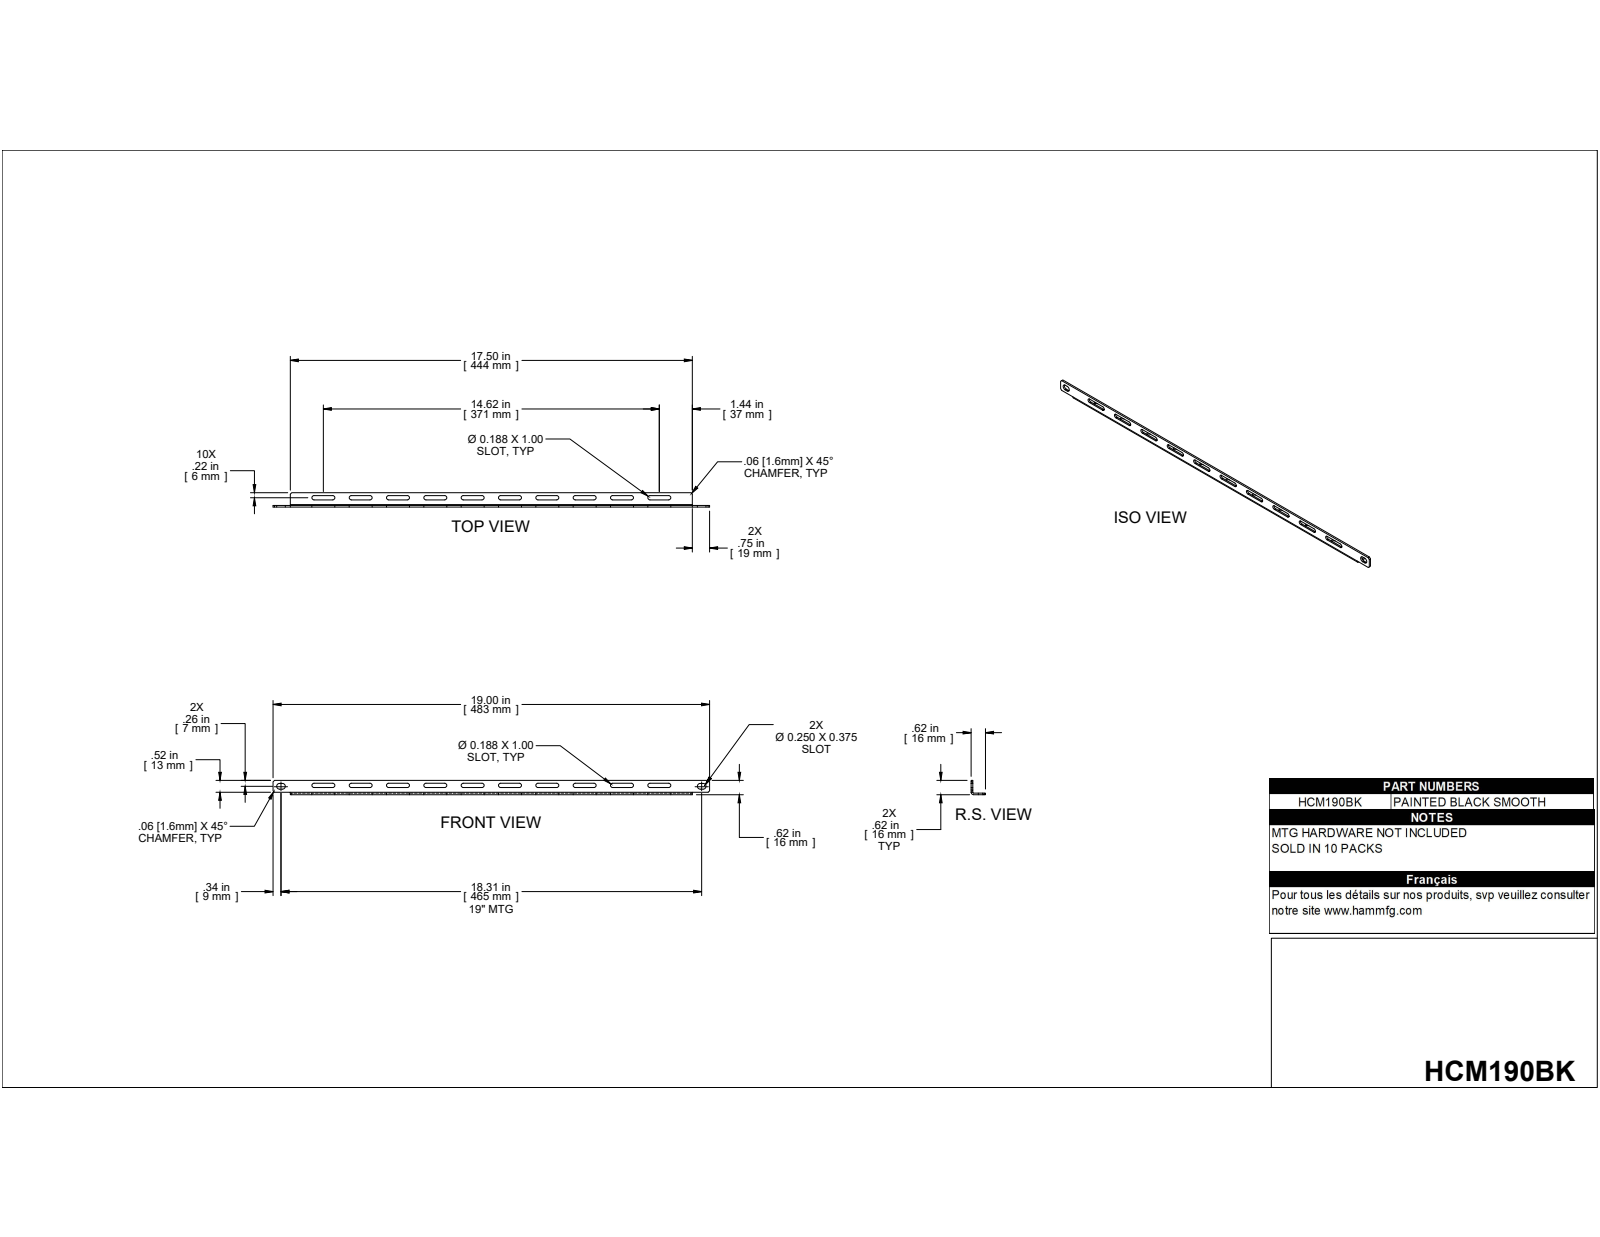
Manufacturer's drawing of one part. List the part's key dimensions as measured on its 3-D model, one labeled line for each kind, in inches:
Part name (STEP PRODUCT): COM57141-1
STEP written by: ST-DEVELOPER v16.7 (AUTOMOTIVE_DESIGN)
Units: inches
Bodies: 1 solid, 108 faces (62 planar, 46 cylindrical, 0 other)
Overall size (bounding box): 19 × 0.625 × 0.625
Volume: 1.23 in³ · Surface area: 40.38 in²
Partial cylindrical surfaces — rounded edges, fillets, slot ends (radius × count): R0.094 ×40, R0.125 ×4, R0.036 ×1, R0.108 ×1
Main face-to-face distances: 0.072, 0.313, 0.553, 0.625, 0.553, 0.625, 0.187, 0.428, 0.5, 0.241
